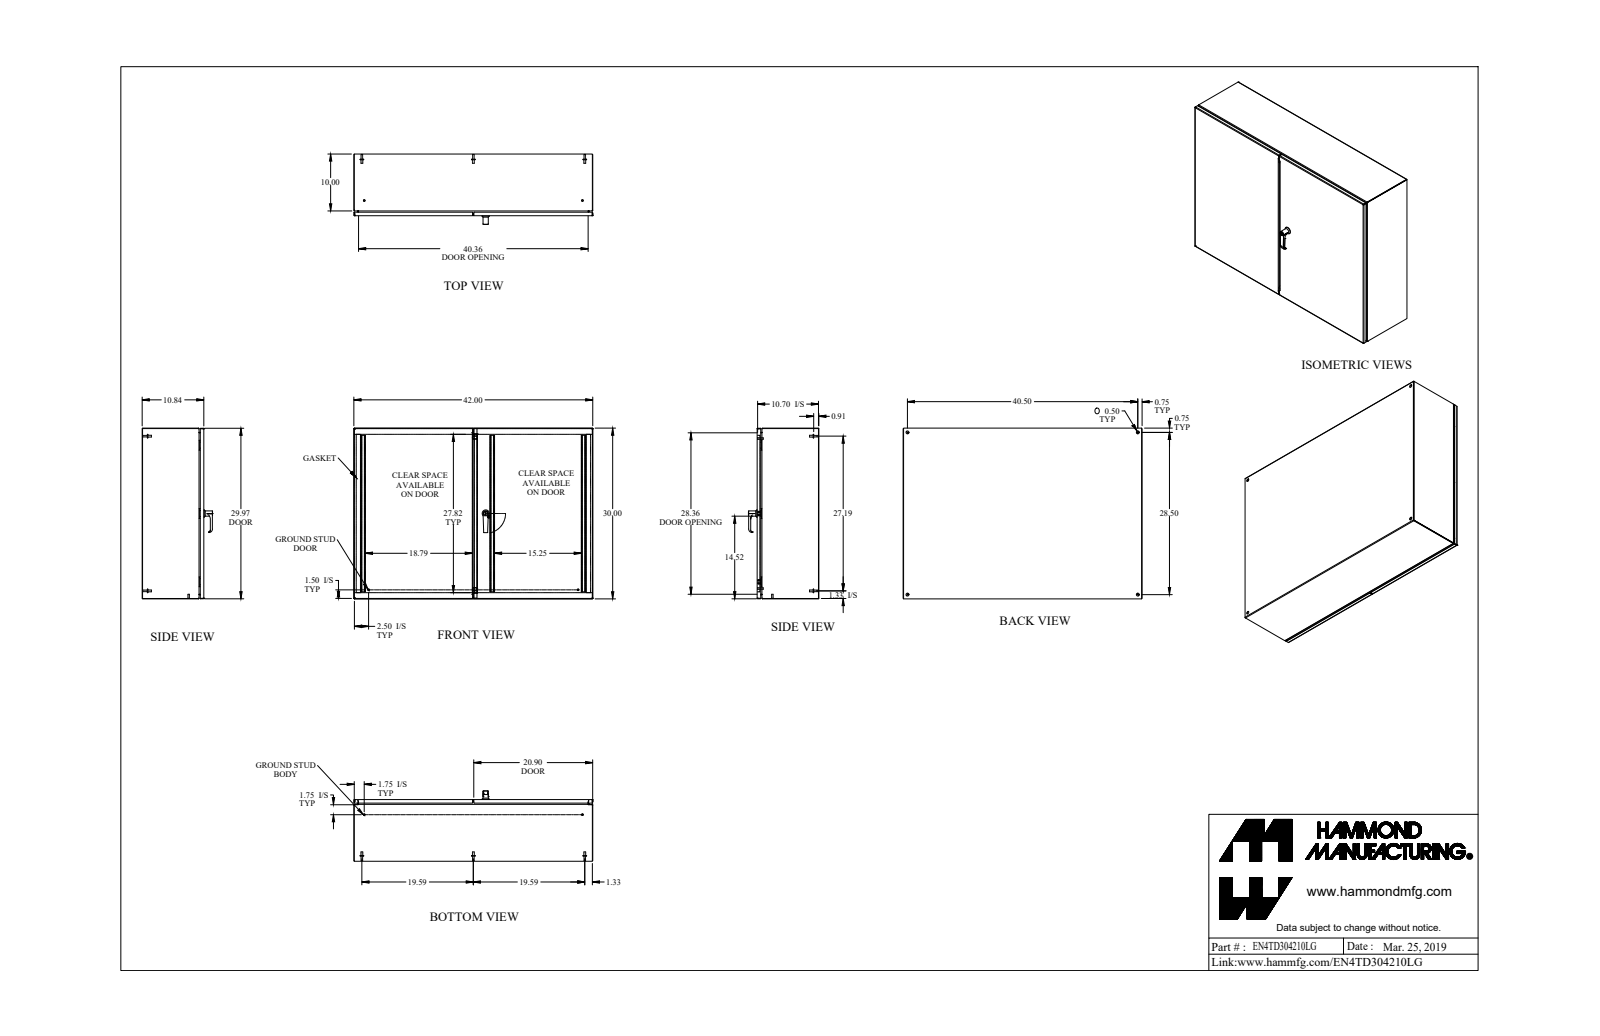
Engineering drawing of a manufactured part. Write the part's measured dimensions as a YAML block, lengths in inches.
part_name: "EN4TD304210LG"
step_written_by: "SolidWorks 2018 (AUTOMOTIVE_DESIGN)"
units: inches
bodies: {solids: 85, faces: 2139, planar: 955, cylindrical: 790, other: 394}
overall_size: [42, 30, 12.372]
volume: 359.7
surface_area: 9434
round_holes:
  - {diameter: 0.196, count: 5}
  - {diameter: 0.176, count: 4}
  - {diameter: 0.265, count: 4}
  - {diameter: 0.5, count: 4}
  - {diameter: 0.24, count: 3}
  - {diameter: 0.242, count: 3}
  - {diameter: 0.172, count: 2}
  - {diameter: 0.25, count: 2}
  - {diameter: 0.256, count: 2}
  - {diameter: 0.26, count: 2}
  - {diameter: 0.313, count: 2}
  - {diameter: 0.394, count: 2}
round_bosses_or_shafts:
  - {diameter: 0.25, count: 12}
  - {diameter: 0.313, count: 8}
  - {diameter: 0.625, count: 6}
  - {diameter: 0.27, count: 6}
  - {diameter: 0.51, count: 4}
  - {diameter: 0.281, count: 4}
  - {diameter: 0.156, count: 4}
  - {diameter: 0.75, count: 3}
partial_cylinders:
  - {radius: 0.063, count: 30}
  - {radius: 0.036, count: 26}
  - {radius: 0.108, count: 26}
  - {radius: 0.094, count: 20}
  - {radius: 0.016, count: 18}
  - {radius: 0.043, count: 18}
  - {radius: 0.081, count: 18}
  - {radius: 0.02, count: 16}
face_to_face_distances: [0.072, 10.77, 10.698, 10.842, 29.928, 41.928, 29.856, 30, 41.856, 42]
hole_center_spacings: [0.786, 13.188, 17.803, 22.756, 23.023, 26.563, 28.5, 40.5]
